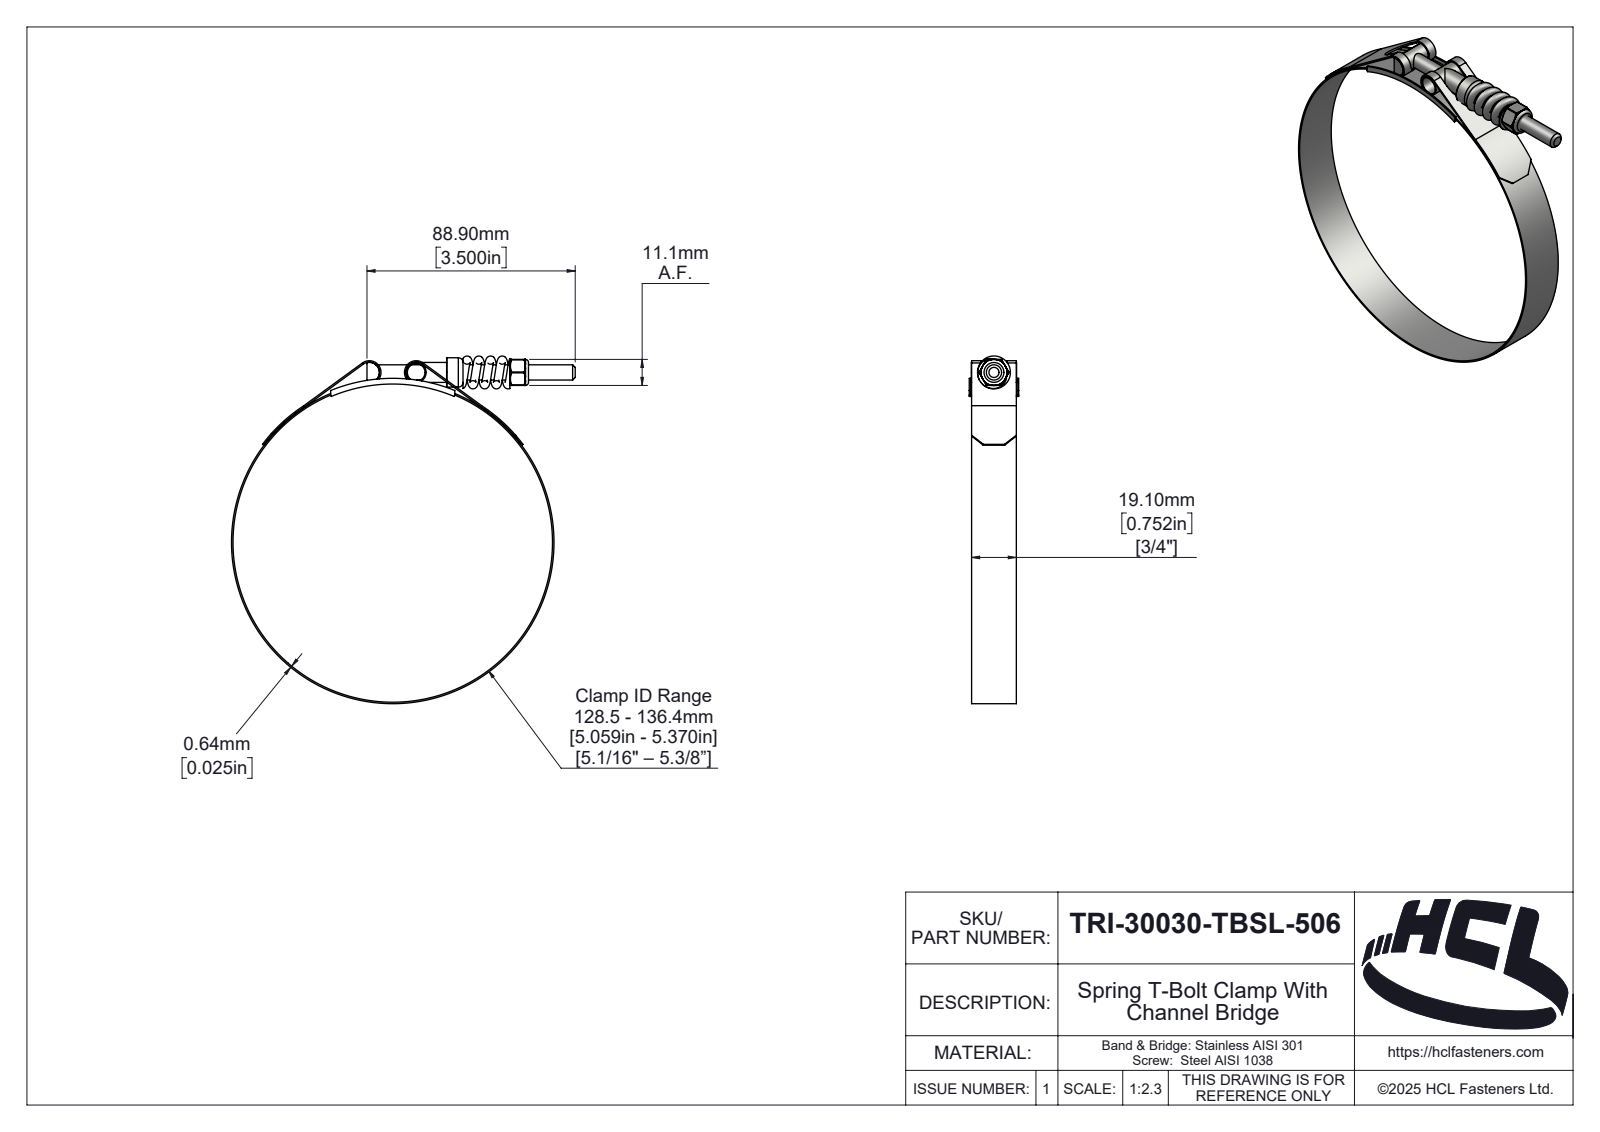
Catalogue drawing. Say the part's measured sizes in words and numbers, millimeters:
The part is named "TRI-30030-TBSL-506". Its 3-D file was written by "SolidWorks 2025 (AUTOMOTIVE_DESIGN)". It is 7 solids with 332 faces: 48 planar, 122 cylindrical and 162 other. Overall it measures 148.38 by 147.74 by 21.1 millimeters. Its volume is 13 697 cubic millimeters and its surface area 30 184 square millimeters. Round holes: 1 of diameter 5.4, 1 of diameter 6.35, 1 of diameter 6.5, 1 of diameter 7.52, 1 of diameter 136.4. Round bosses or shafts: 2 of diameter 8.52, 1 of diameter 137.68, 1 of diameter 12.52. Partial cylindrical surfaces (rounded edges, fillets, slot ends): 6 of radius 0.39, 2 of radius 0.5, 2 of radius 4.36, 2 of radius 5, 1 of radius 0.59, 1 of radius 2.42, 1 of radius 3.03, 1 of radius 3.19. The main face-to-face distances are 0.64, 19.1, 1, 20.1, 20.46, 0.36, 19.46, 21.1, 61, 11.11. The hole center spacings are 73.2.
